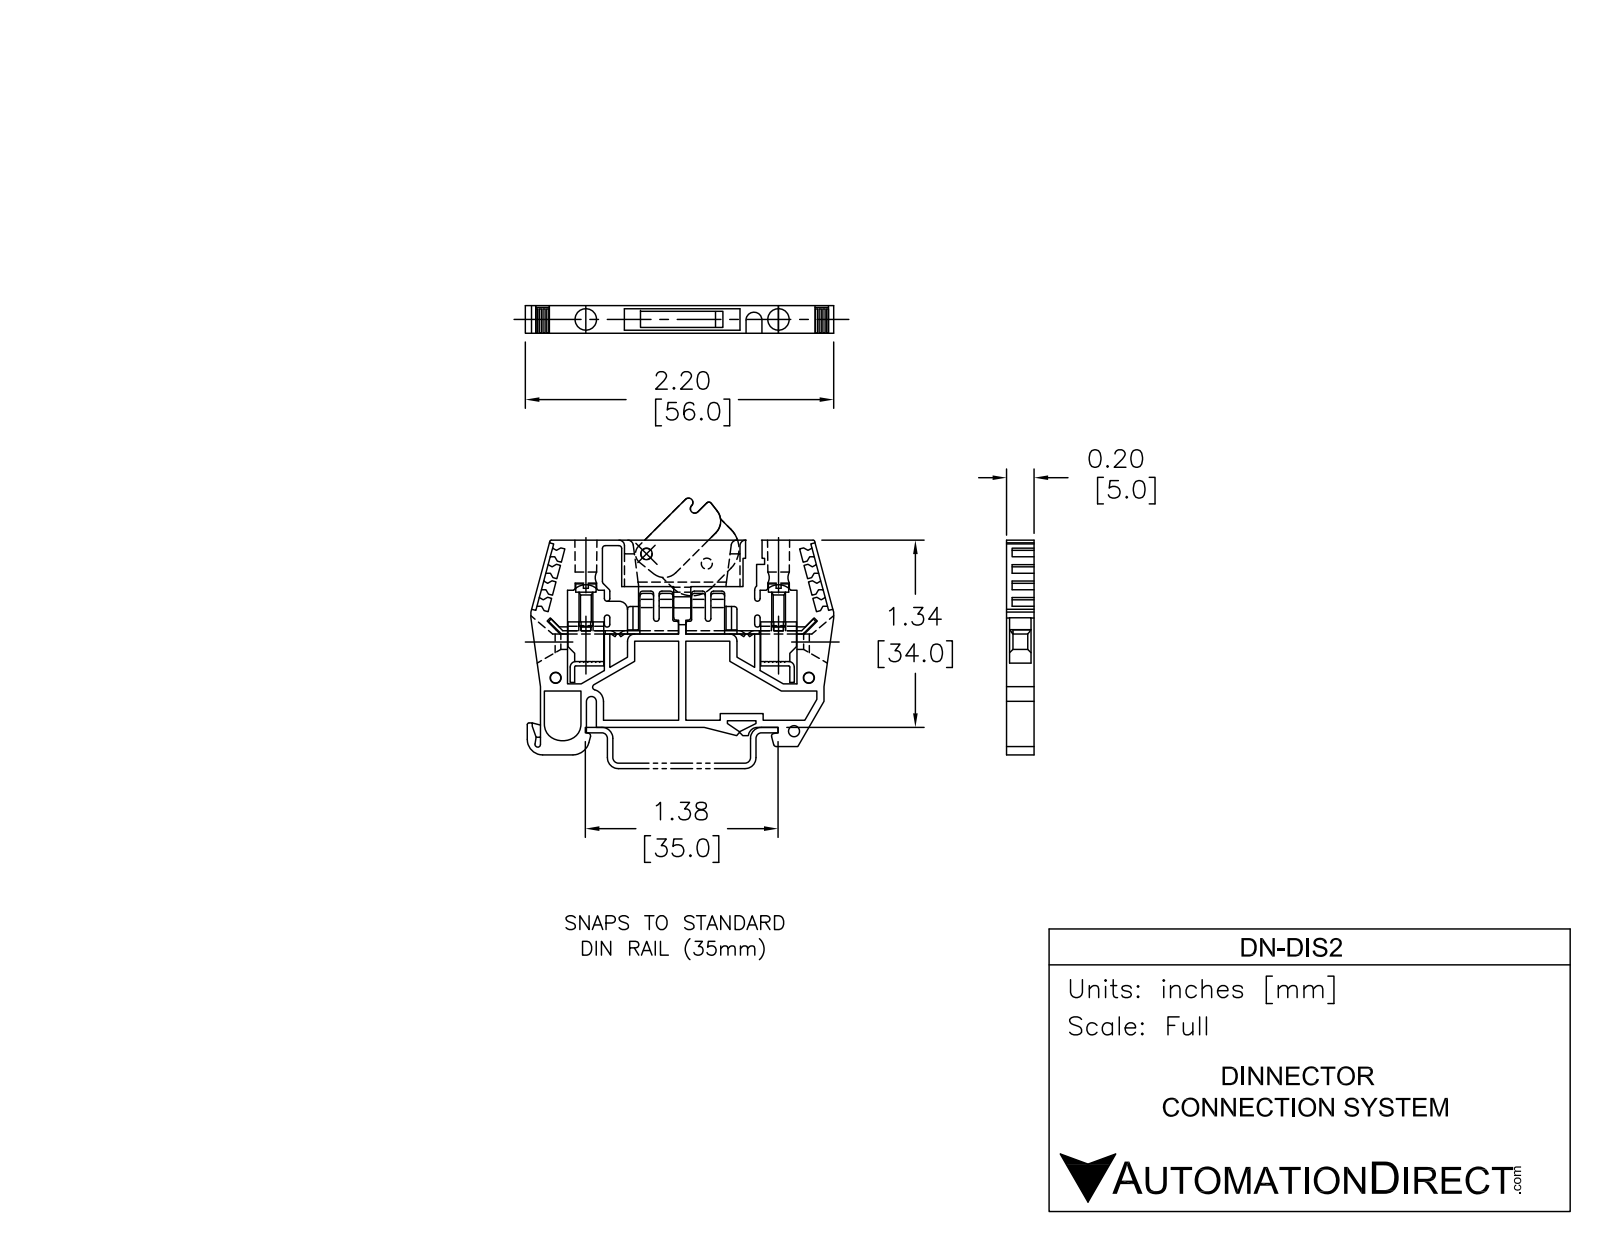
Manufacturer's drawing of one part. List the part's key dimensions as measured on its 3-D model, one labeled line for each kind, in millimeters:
Part name (STEP PRODUCT): 4258000_DN-QFE2_1; 4358003_DN-DIS2; 435K0001
STEP written by: SolidWorks 2013 (AUTOMOTIVE_DESIGN)
Units: millimetres
Bodies: 2 solids, 347 faces (218 planar, 88 cylindrical, 41 other)
Overall size (bounding box): 55.65 × 39 × 5.05
Volume: 7 936 mm³ · Surface area: 6 489 mm²
Round holes (diameter × count): ⌀2 ×4, ⌀4.1 ×2
Round bosses / shafts (diameter × count): ⌀2 ×1
Partial cylindrical surfaces — rounded edges, fillets, slot ends (radius × count): R0.5 ×22, R3 ×7, R1 ×3, R0.8 ×2, R5 ×2, R0.9 ×1, R1.05 ×1, R1.5 ×1
Main face-to-face distances: 5, 2.2, 0.6, 34, 2.85, 4.45, 0.55, 1, 2.15, 2.25
Hole centre spacings: 10.07, 26.45, 26.89, 30.67, 35, 44.38, 46
